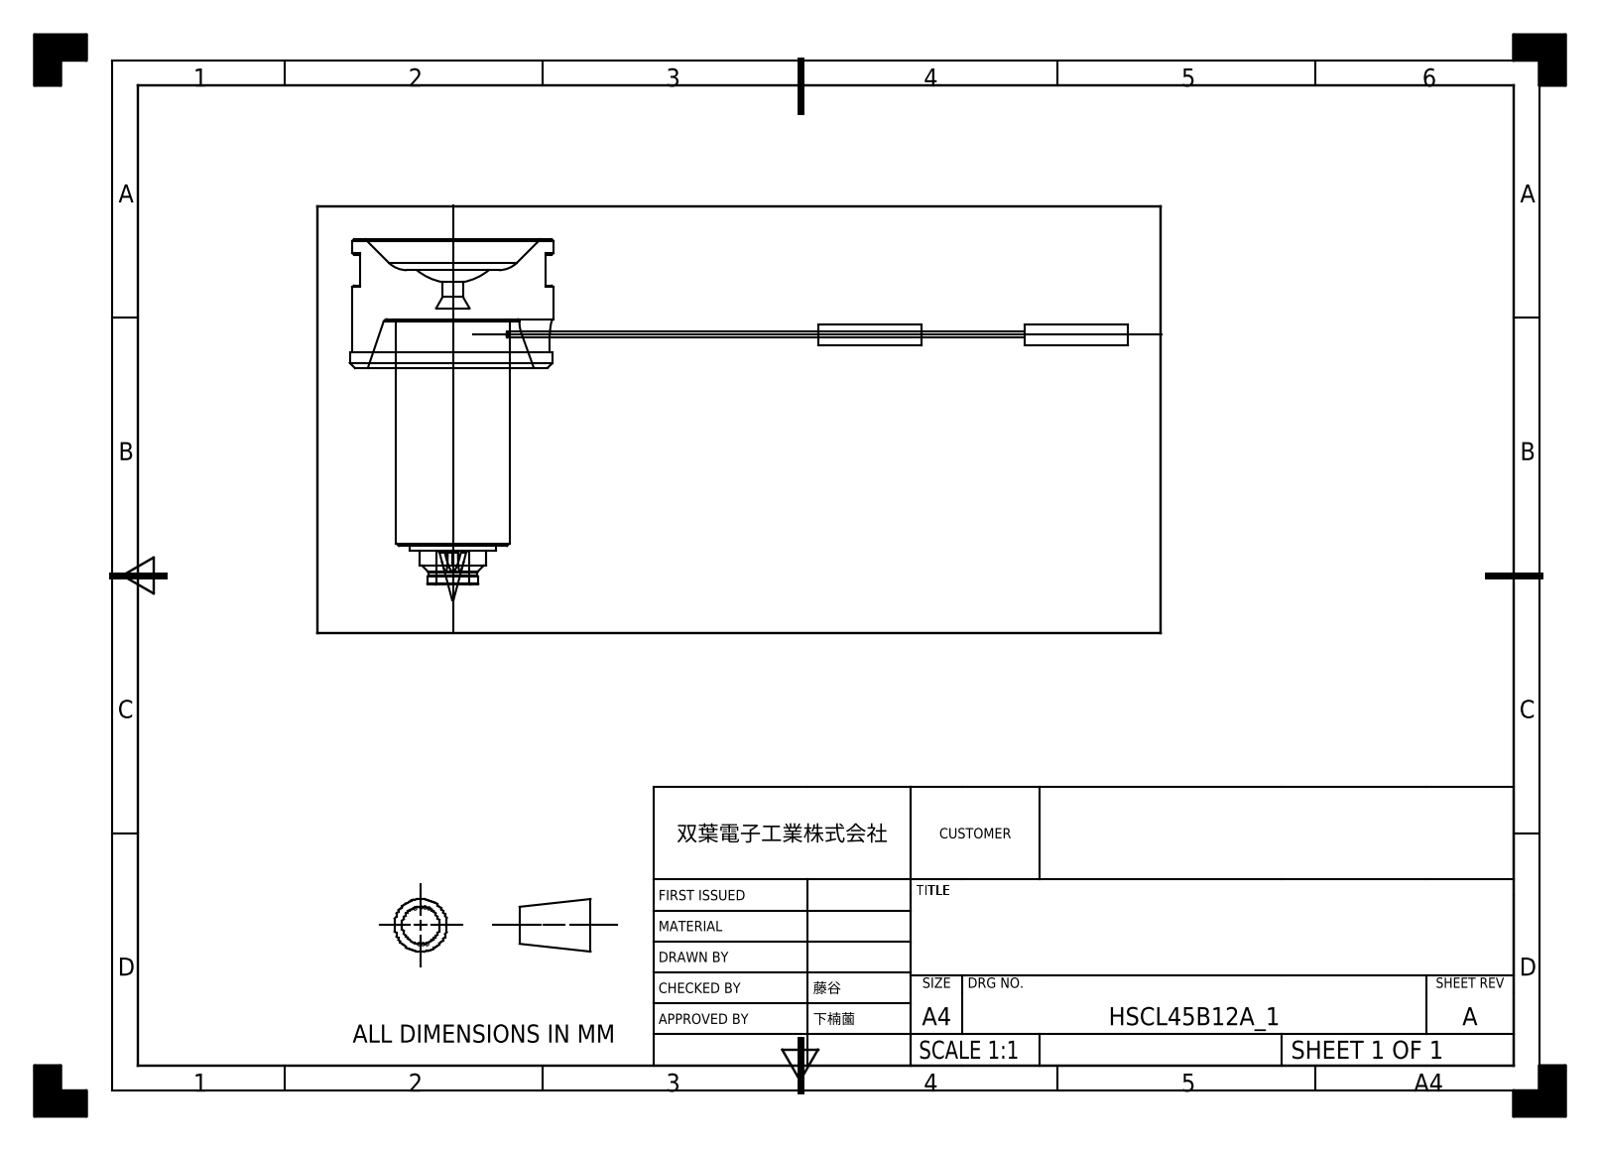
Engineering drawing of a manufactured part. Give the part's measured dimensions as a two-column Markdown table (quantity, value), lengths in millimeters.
| quantity | value |
| --- | --- |
| part name | HSCL45B12A |
| STEP written by | SIEMENS PLM Software NX 2023 (AUTOMOTIVE_DESIGN) |
| units | millimeters |
| bodies | 5 solids, 75 faces (34 planar, 23 cylindrical, 18 other) |
| overall size | 156.5 × 70 × 46 |
| volume | 51 627 mm³ |
| surface area | 13 510 mm² |
| round holes (diameter × count) | 4 × 1, 9.5 × 1 |
| round bosses / shafts (diameter × count) | 4 × 2, 1.2 × 2, 46 × 1, 45 × 1, 27 × 1, 23.8 × 1, 12 × 1, 11.6 × 1 |
| partial cylindrical surfaces (radius × count) | 2.8 × 3, 3 × 2, 10.9 × 1 |
| main face-to-face distances | 19, 6, 9.5, 25, 45, 63.7, 57.7, 38.7, 15.5, 48.2 |
